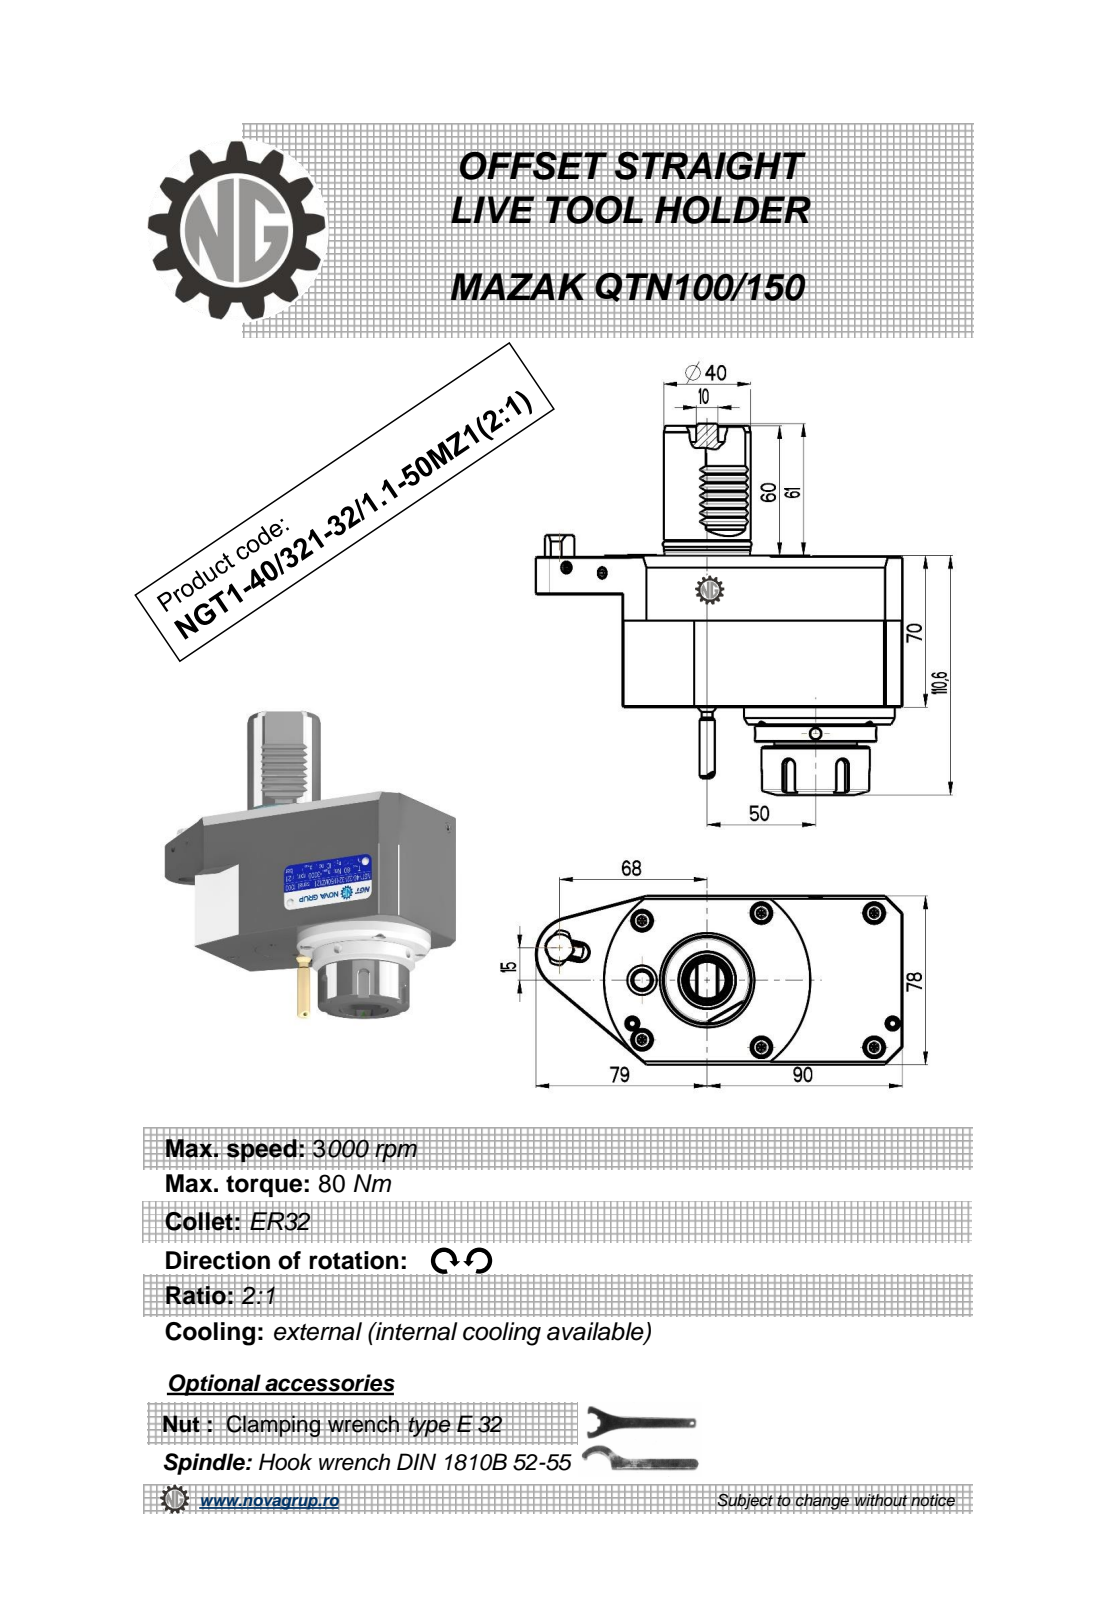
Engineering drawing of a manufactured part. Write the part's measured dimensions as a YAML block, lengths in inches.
part_name: "NGT1_40_321_32_1_1_50MZ1"
step_written_by: "PRO/ENGINEER BY PARAMETRIC TECHNOLOGY CORPORATION, 2010280 (CONFIG_CONTROL_DESIGN)"
units: inches
bodies: {solids: 1, faces: 267, planar: 112, cylindrical: 68, other: 87}
overall_size: [6.756, 6.654, 3.071]
volume: 53.75
surface_area: 113.7
round_holes:
  - {diameter: 0.197, count: 2}
  - {diameter: 0.098, count: 1}
  - {diameter: 0.118, count: 1}
  - {diameter: 0.315, count: 1}
  - {diameter: 1.024, count: 1}
  - {diameter: 1.063, count: 1}
round_bosses_or_shafts:
  - {diameter: 2.874, count: 1}
  - {diameter: 2.205, count: 1}
  - {diameter: 1.969, count: 1}
  - {diameter: 1.693, count: 1}
  - {diameter: 1.614, count: 1}
  - {diameter: 1.575, count: 1}
  - {diameter: 1.551, count: 1}
  - {diameter: 1.425, count: 1}
partial_cylinders:
  - {radius: 0.012, count: 7}
  - {radius: 0.006, count: 6}
  - {radius: 0.118, count: 5}
  - {radius: 0.031, count: 2}
  - {radius: 0.315, count: 1}
  - {radius: 0.354, count: 1}
  - {radius: 0.687, count: 1}
face_to_face_distances: [3.071, 2.756, 0.315, 5.079, 0.709, 2.362, 2.047, 0.295, 3.469, 0.335]
hole_center_spacings: [0.846, 1.181, 1.453, 1.969, 2.143, 3.15]
